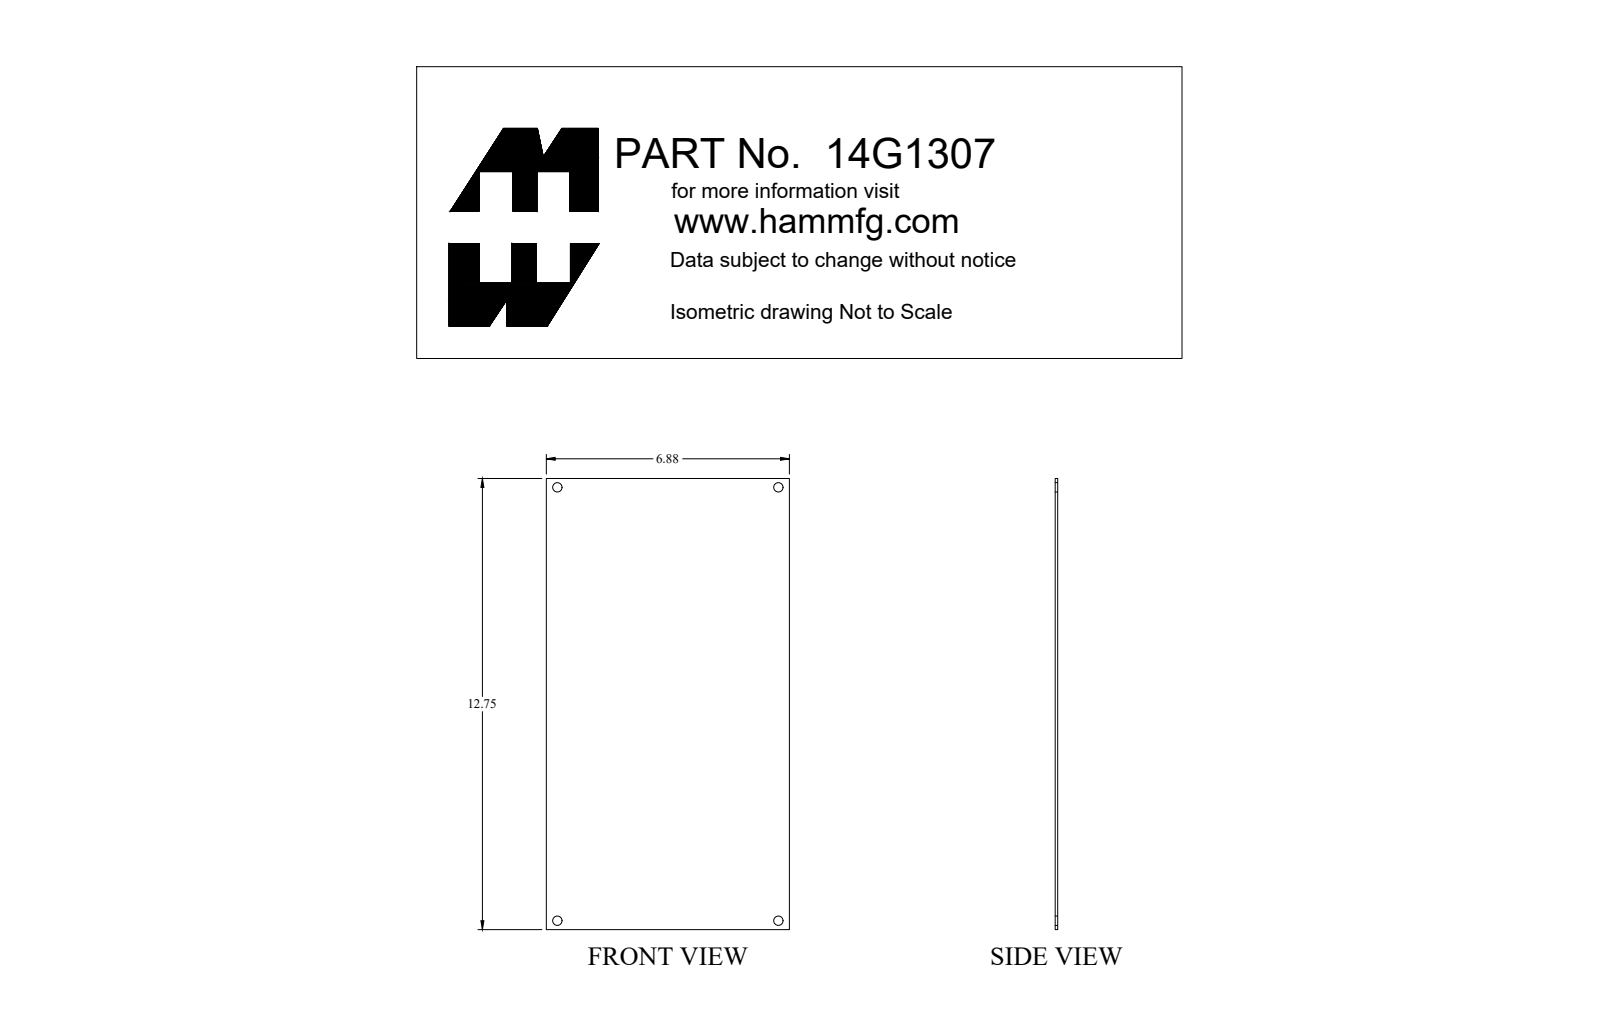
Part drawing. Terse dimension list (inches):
name: 14G1307
written by: SolidWorks 2018 (AUTOMOTIVE_DESIGN)
unit: in
bodies: 1 solid, 10 faces (6 planar, 4 cylindrical, 0 other)
size: 12.75 × 6.875 × 0.072
volume: 6.295 in³; area: 177.9 in²
holes: 4× ⌀0.265
face distances: 0.072, 6.875, 12.75
hole spacings: 6.25, 12.25, 13.752
